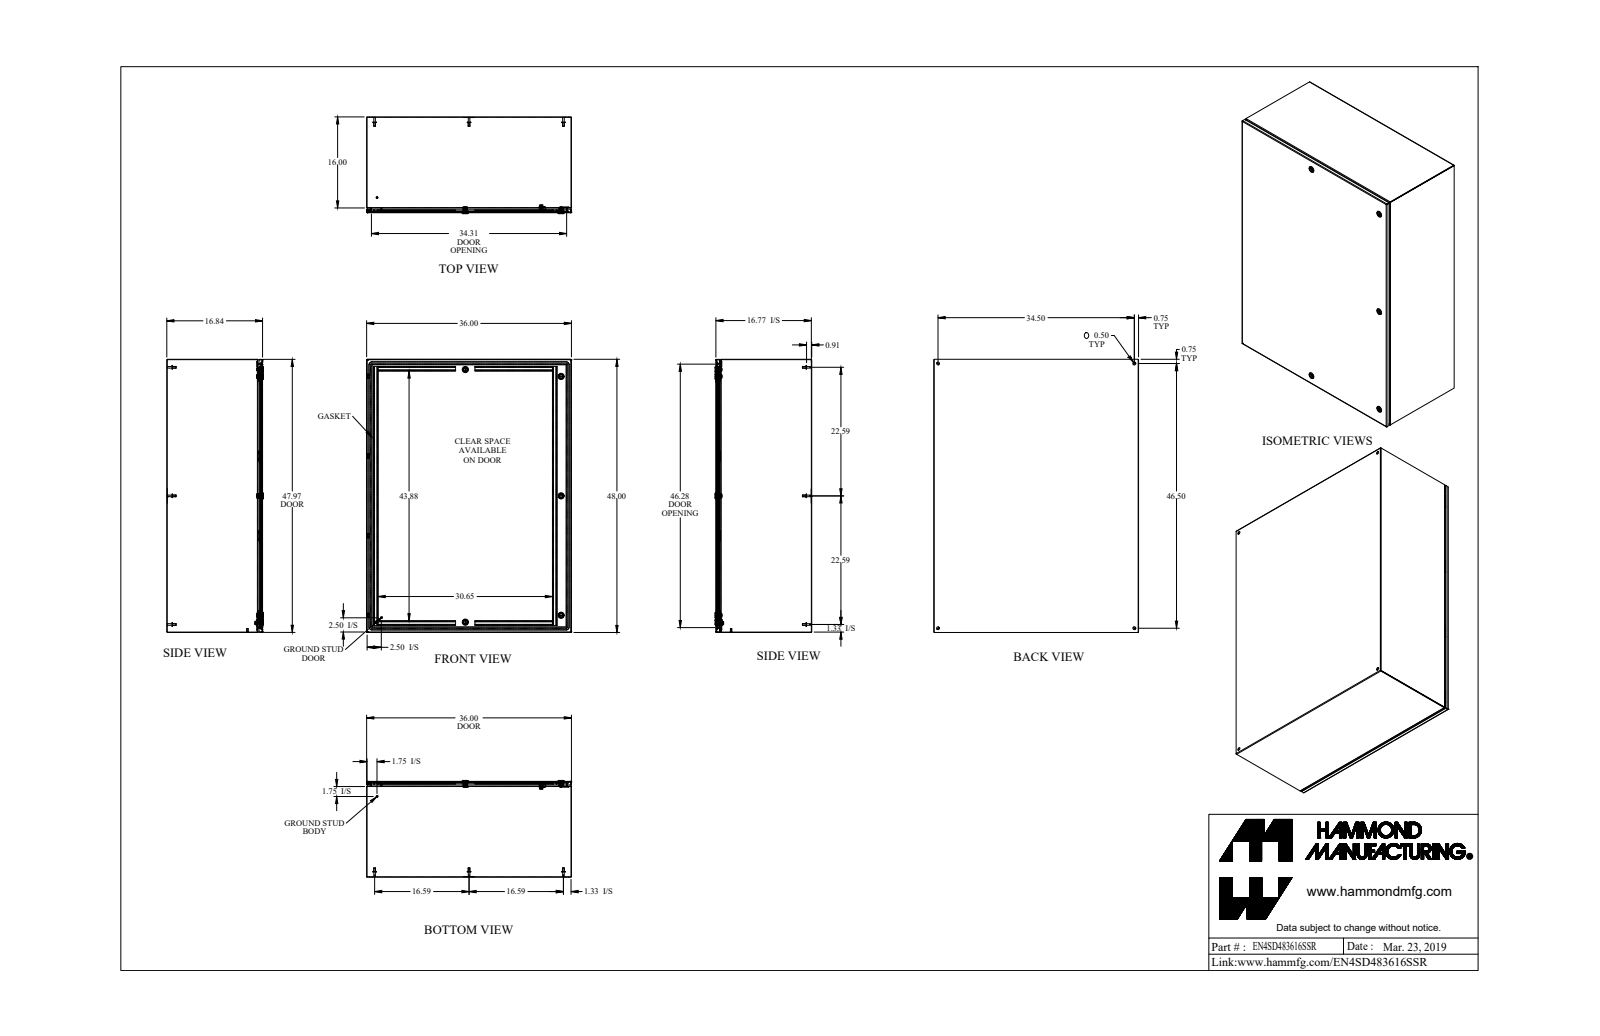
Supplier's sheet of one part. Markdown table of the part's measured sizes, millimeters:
| quantity | value |
| --- | --- |
| part name | EN4SD483616SSR |
| STEP written by | SolidWorks 2018 (AUTOMOTIVE_DESIGN) |
| units | millimeters |
| bodies | 66 solids, 1714 faces (896 planar, 545 cylindrical, 273 other) |
| overall size | 1219.2 × 914.4 × 431.9 |
| volume | 8 138 000 mm³ |
| surface area | 9 021 000 mm² |
| round holes (diameter × count) | 12.7 × 9, 5 × 5, 9.8 × 5, 16 × 5, 19.5 × 5, 4.4 × 2, 5 × 1, 6.1 × 1, 6.1 × 1, 7 × 1, 9.5 × 1 |
| round bosses / shafts (diameter × count) | 8 × 10, 15.9 × 9, 7 × 8, 27.9 × 5, 15.9 × 5, 6 × 5, 19.9 × 3, 13.3 × 3 |
| partial cylindrical surfaces (radius × count) | 1.2 × 32, 0.3 × 24, 0.9 × 18, 2.7 × 18, 1.6 × 17, 2.4 × 10, 3.2 × 10, 0.4 × 9 |
| main face-to-face distances | 1.8, 426, 424.1, 427.8, 912.6, 910.7, 914.4, 1.8, 1215.5, 1217.4 |
| hole center spacings | 422.2, 428.8, 455.8, 591.2, 707.5, 851, 876.3, 1034.2 |
